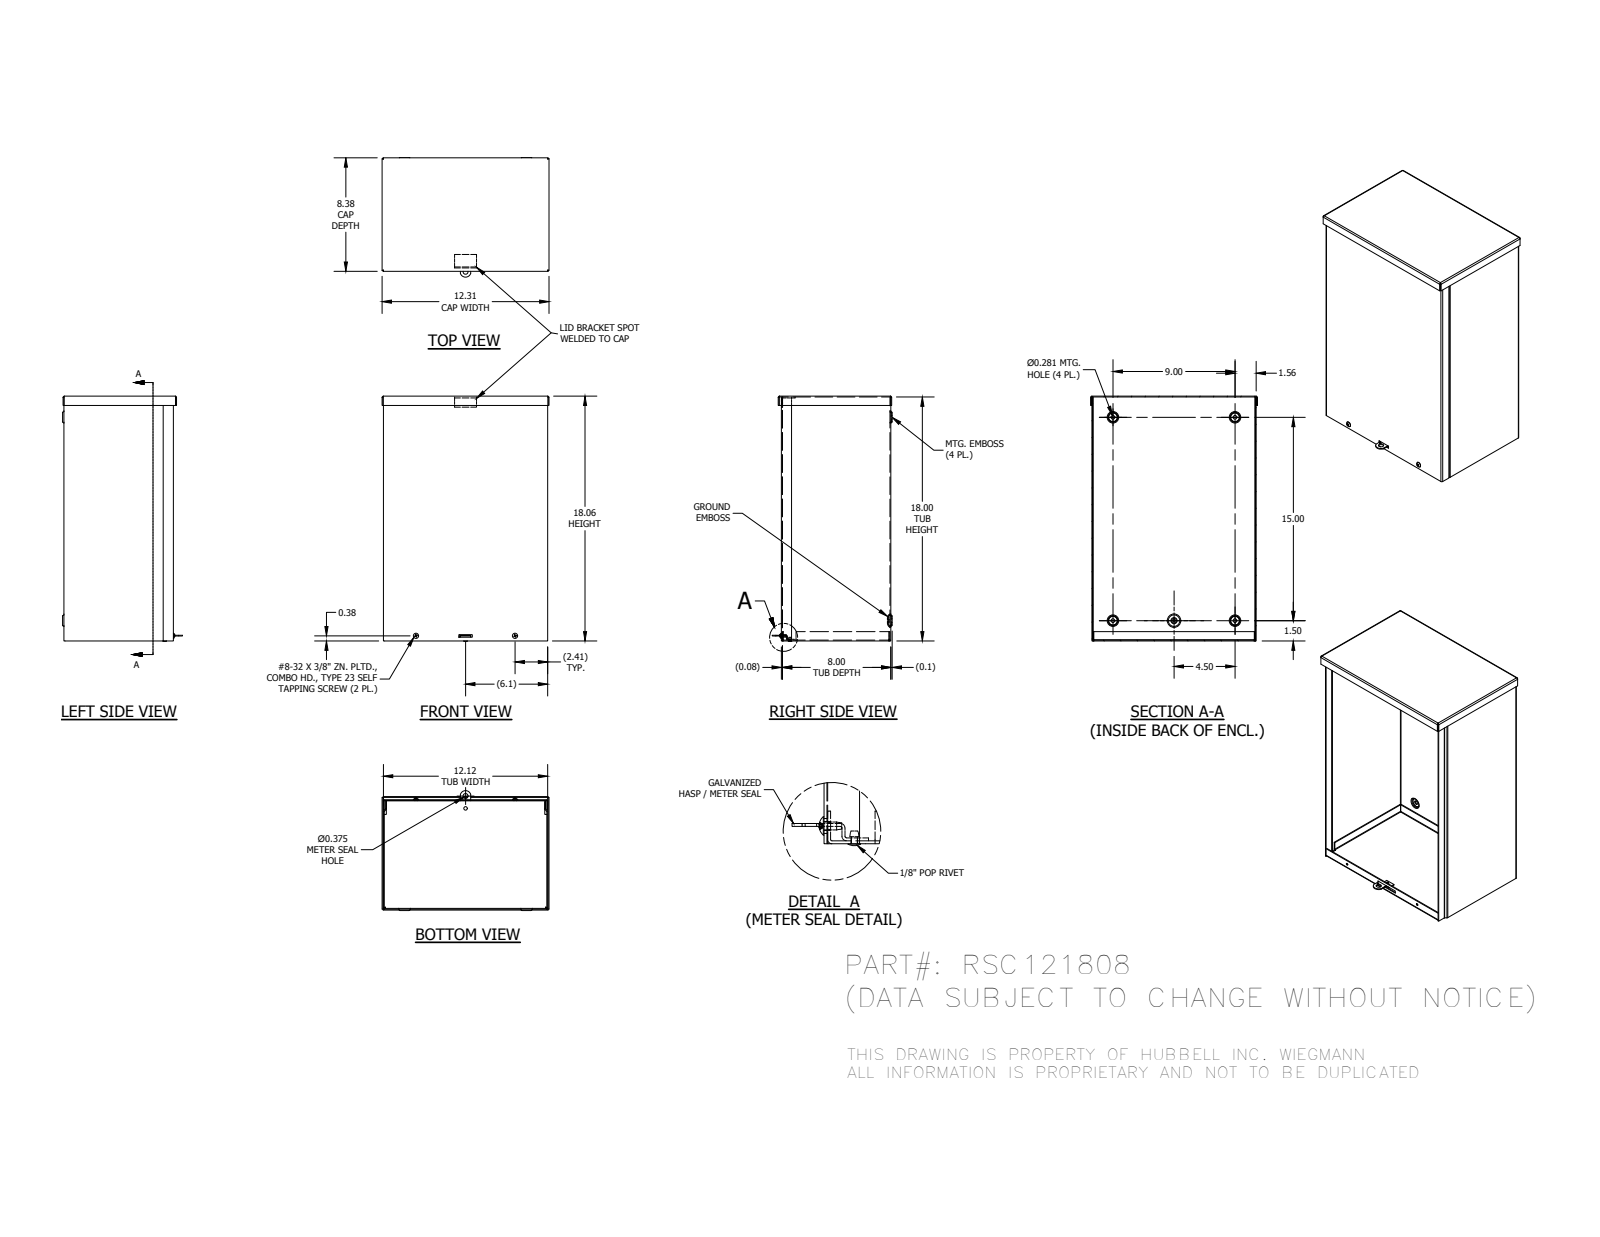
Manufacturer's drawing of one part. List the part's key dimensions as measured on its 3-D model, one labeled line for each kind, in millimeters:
Part name (STEP PRODUCT): RSC121808BKPA; RSC1208EWPA; RSC1218LFA; RSC1208CPA (+5 more)
STEP written by: Autodesk Inventor 2014 (AUTOMOTIVE_DESIGN)
Units: millimetres
Bodies: 9 solids, 320 faces (183 planar, 61 cylindrical, 76 other)
Overall size (bounding box): 459.79 × 312.71 × 224.8
Volume: 1 012 000 mm³ · Surface area: 1 296 000 mm²
Round holes (diameter × count): ⌀7.14 ×4, ⌀7.94 ×4, ⌀3.73 ×2, ⌀3.17 ×1, ⌀3.45 ×1, ⌀4.34 ×1, ⌀9.52 ×1
Round bosses / shafts (diameter × count): ⌀9.75 ×2, ⌀4.17 ×2, ⌀6.65 ×1, ⌀5.93 ×1, ⌀3.17 ×1
Partial cylindrical surfaces — rounded edges, fillets, slot ends (radius × count): R0.79 ×19, R2.37 ×18, R2.67 ×1, R10.16 ×1
Main face-to-face distances: 1.57, 203.6, 306.37, 205.17, 202.03, 457.2, 304.8, 307.94, 458.77, 455.63
Hole centre spacings: 209.13, 35.71, 35.72, 97.17, 114.3, 185.74, 228.6, 381
